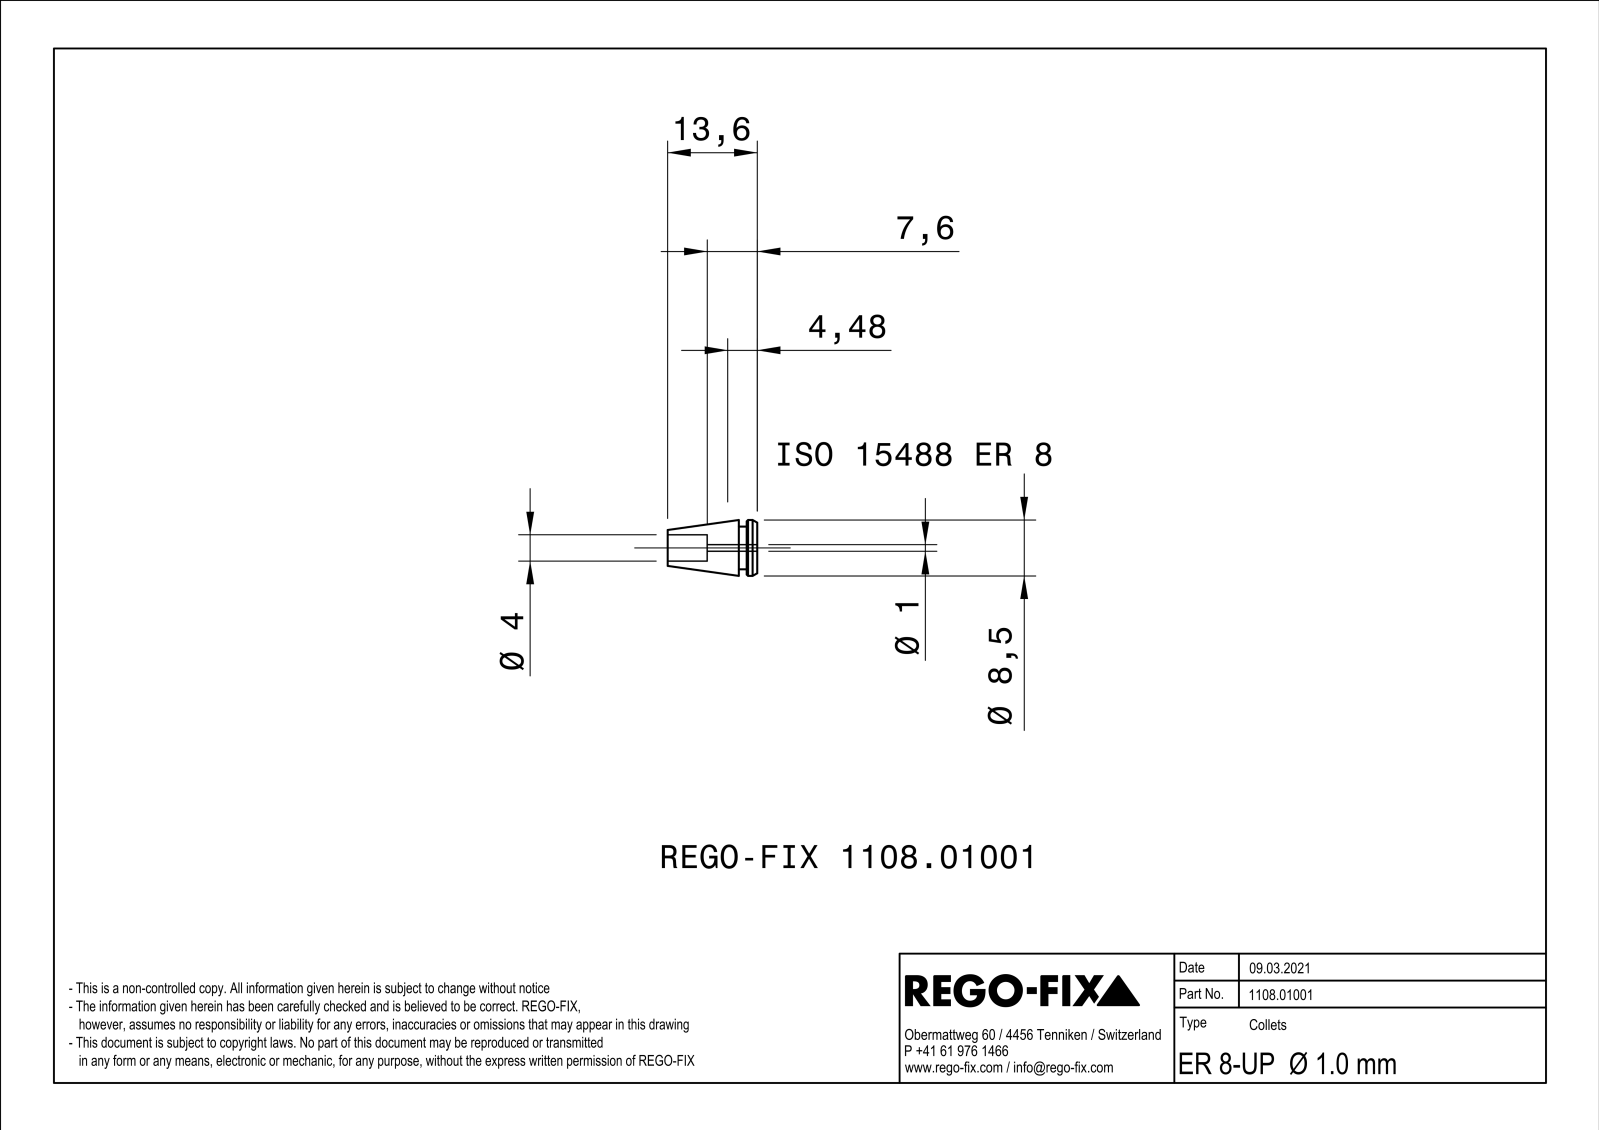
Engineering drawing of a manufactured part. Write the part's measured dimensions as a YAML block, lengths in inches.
part_name: "NOCUT"
step_written_by: "SIEMENS PLM Software Solid Edge ST10 (AUTOMOTIVE_DESIGN)"
units: inches
bodies: {solids: 1, faces: 239, planar: 89, cylindrical: 37, other: 113}
overall_size: [0.535, 0.334, 0.334]
volume: 0.021
surface_area: 1.52
round_holes:
  - {diameter: 0.039, count: 1}
round_bosses_or_shafts:
  - {diameter: 0.335, count: 1}
partial_cylinders:
  - {radius: 0.787, count: 4}
  - {radius: 0.079, count: 1}
  - {radius: 0.128, count: 1}
face_to_face_distances: [0.018, 0.018, 0.017, 0.11, 0.063, 0.047, 0.236, 0.299, 0.189, 0.535]
